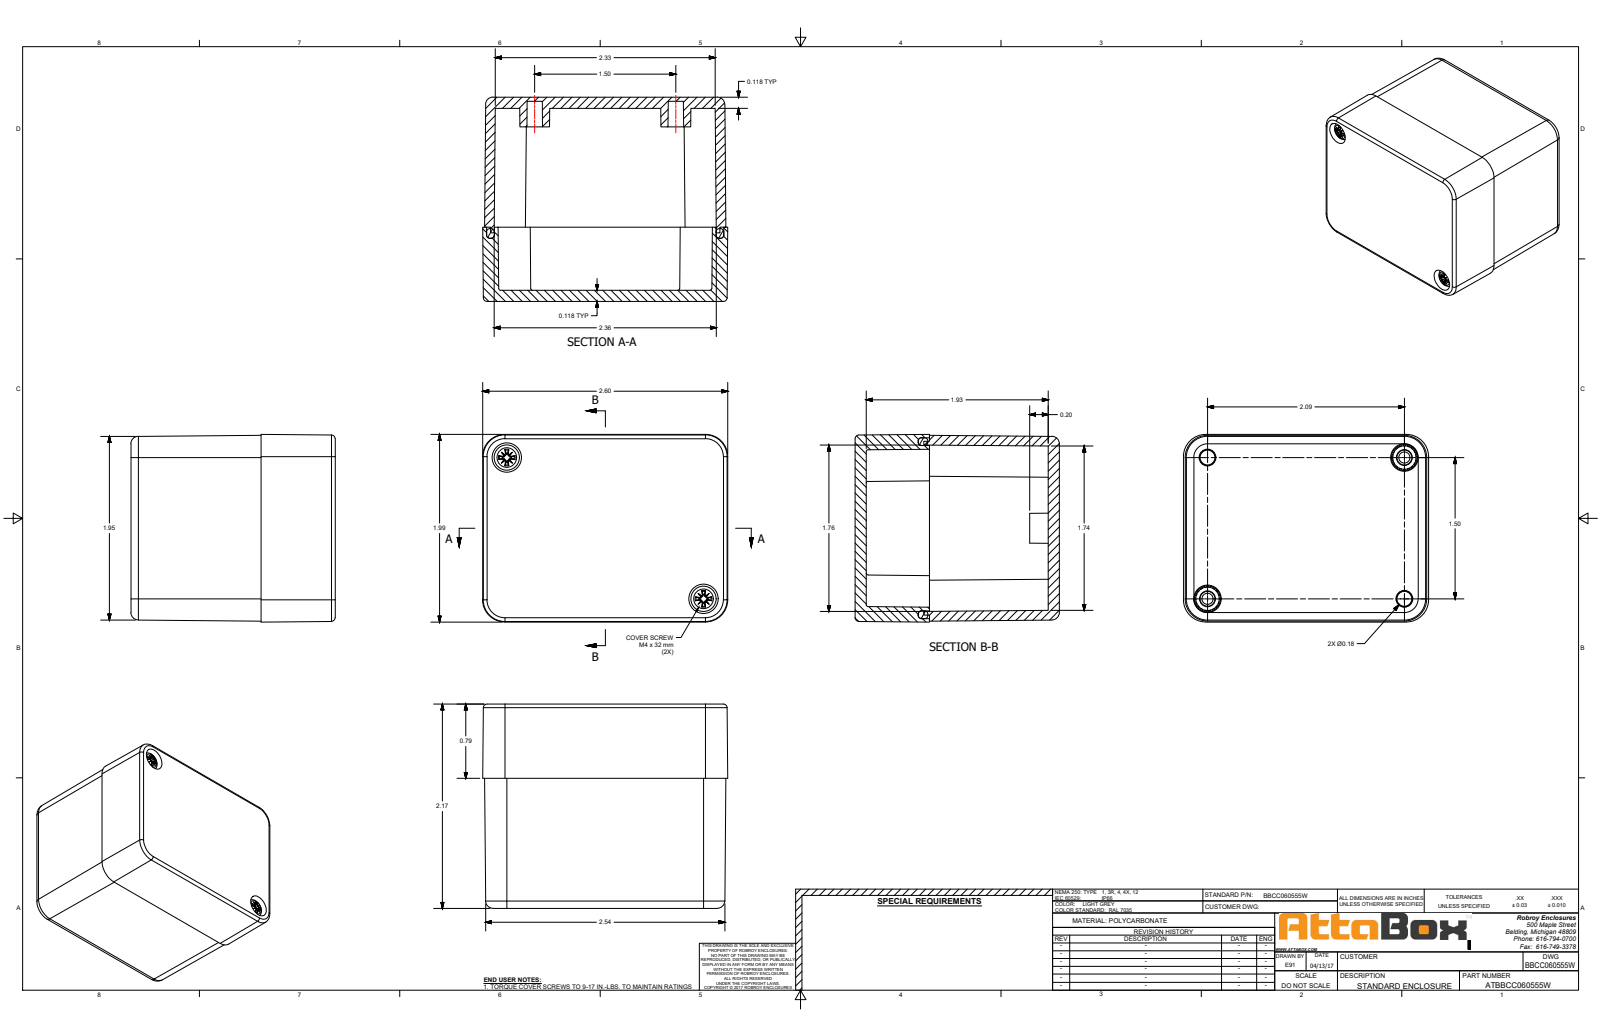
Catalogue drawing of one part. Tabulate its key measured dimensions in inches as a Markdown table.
| quantity | value |
| --- | --- |
| part name | BBCC060555W |
| STEP written by | SolidWorks 2018 (AUTOMOTIVE_DESIGN) |
| units | inches |
| bodies | 7 solids, 961 faces (341 planar, 250 cylindrical, 370 other) |
| overall size | 2.598 × 2.165 × 1.988 |
| volume | 3.619 in³ |
| surface area | 67.48 in² |
| round holes (diameter × count) | 0.177 × 4, 0.291 × 4, 0.128 × 2, 0.193 × 2, 0.201 × 2, 0.276 × 2, 0.311 × 2 |
| round bosses / shafts (diameter × count) | 0.268 × 2, 0.173 × 2, 0.157 × 2, 0.13 × 2 |
| partial cylindrical surfaces (radius × count) | 0.035 × 48, 0.02 × 8, 0.098 × 8, 0.181 × 8, 0.039 × 4, 0.079 × 4, 0.114 × 4, 0.197 × 4 |
| main face-to-face distances | 0.118, 2.047, 0.102, 2.165, 1.929, 1.978, 1.876, 2.476, 2.579, 1.378 |
| hole center spacings | 1.496, 2.087, 2.568 |
